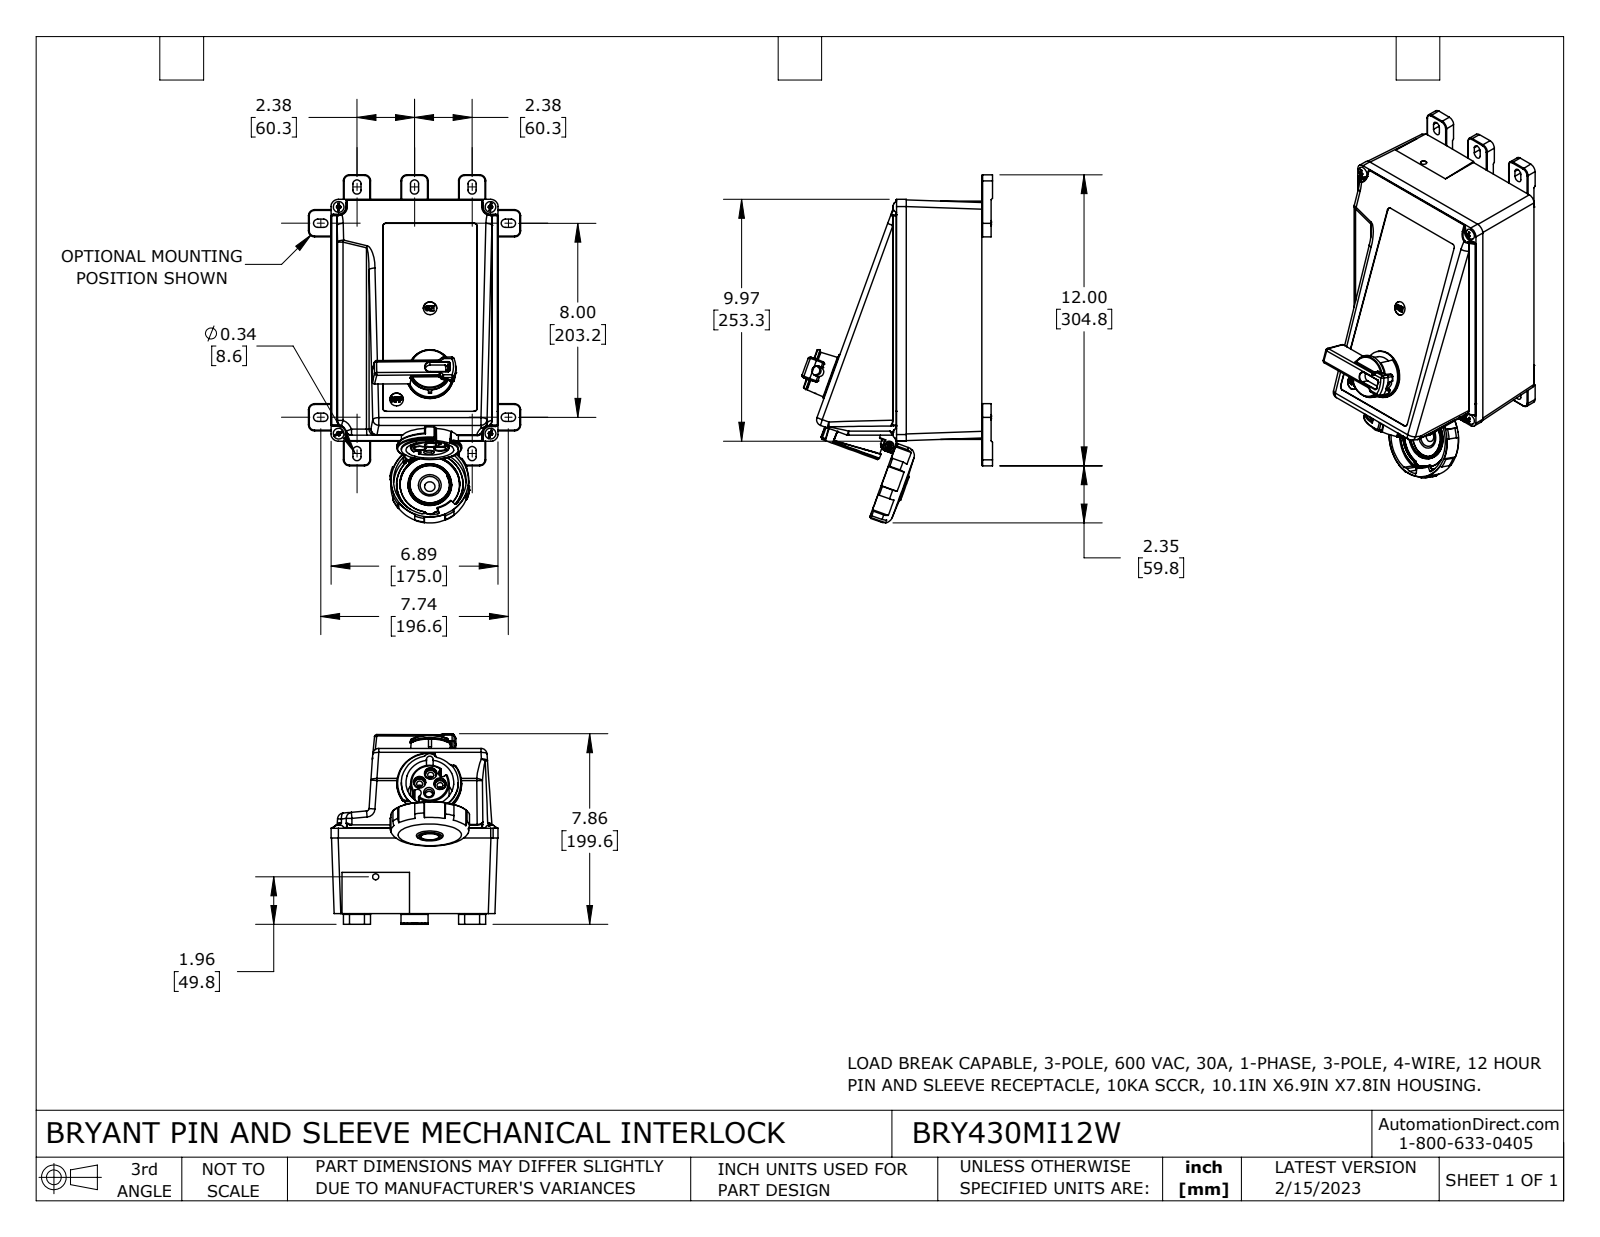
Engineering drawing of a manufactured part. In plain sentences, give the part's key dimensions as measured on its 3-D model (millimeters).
The part is named "BRY430MI12W". Its 3-D file was written by "SolidWorks 2021 (CONFIG_CONTROL_DESIGN)". It is 10 solids with 2065 faces: 740 planar, 671 cylindrical and 654 other. Overall it measures 364.6 by 199.6 by 175 millimeters. Its volume is 5 488 000 cubic millimeters and its surface area 300 000 square millimeters. Round holes: 5 of diameter 7.1, 4 of diameter 2, 3 of diameter 6.3, 2 of diameter 4, 2 of diameter 14.2, 1 of diameter 2.6, 1 of diameter 3.5, 1 of diameter 4, 1 of diameter 6.4, 1 of diameter 6.9, 1 of diameter 8.3, 1 of diameter 16.8. Round bosses or shafts: 2 of diameter 6.7, 2 of diameter 3.1, 1 of diameter 69.6, 1 of diameter 59.7, 1 of diameter 48.8, 1 of diameter 45.6, 1 of diameter 40.3, 1 of diameter 31.6. Partial cylindrical surfaces (rounded edges, fillets, slot ends): 124 of radius 0.4, 54 of radius 0.8, 30 of radius 2, 24 of radius 6.4, 17 of radius 2.3, 16 of radius 0.3, 12 of radius 1.9, 10 of radius 4.3. The main face-to-face distances are 3, 245.2, 120.7, 249.7, 4.4, 105.9, 105.6, 3.8, 9.7, 0.9. The hole center spacings are 17.8, 10.7, 25.8, 10.7, 12.1, 15.2, 15.2, 17.
